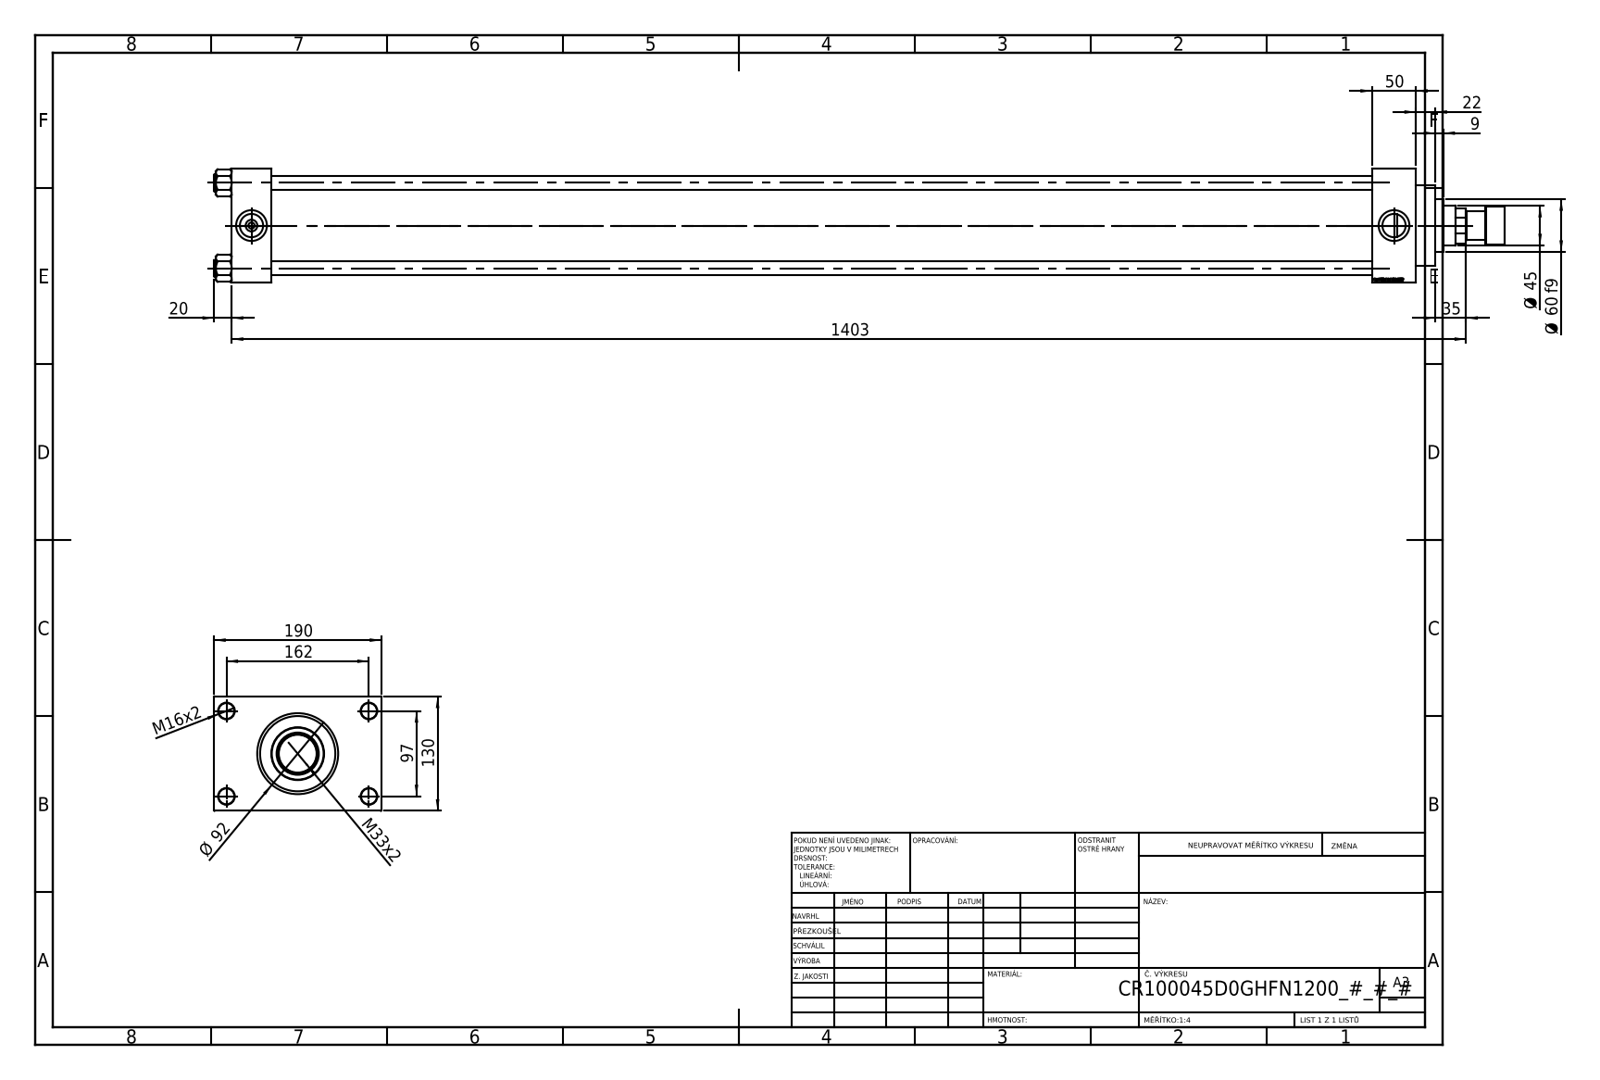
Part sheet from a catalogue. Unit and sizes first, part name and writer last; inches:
Units: inches
Overall size (bounding box): 57.756 × 7.48 × 5.118
Round holes (diameter × count): ⌀0.63 ×4, ⌀0.709 ×4, ⌀0.276 ×2, ⌀1.041 ×2, ⌀1.378 ×2, ⌀1.24 ×1, ⌀1.772 ×1, ⌀1.89 ×1, ⌀2.992 ×1, ⌀3.366 ×1, ⌀3.937 ×1
Round bosses / shafts (diameter × count): ⌀0.748 ×4, ⌀4.173 ×1, ⌀3.622 ×1, ⌀2.362 ×1, ⌀1.732 ×1, ⌀1.299 ×1
Main face-to-face distances: 5.118, 1.772, 51.024, 49.252, 52.992, 51.22, 1.969, 1.181, 6.299, 3.78
Hole centre spacings: 1.281, 2.698, 3.717, 3.815, 4.026, 5.096, 6.367, 3.819
Volume: 403.6 in³ · Surface area: 2 373 in²
Bodies: 12 solids, 1164 faces (548 planar, 92 cylindrical, 524 other)
Part name (STEP PRODUCT): V215CR_VCP_D; V215CR_ROD_END_F; V215_VC_A; V215CR_D_TYCINKA (+2 more)
STEP written by: SolidWorks 2019 (CONFIG_CONTROL_DESIGN)
